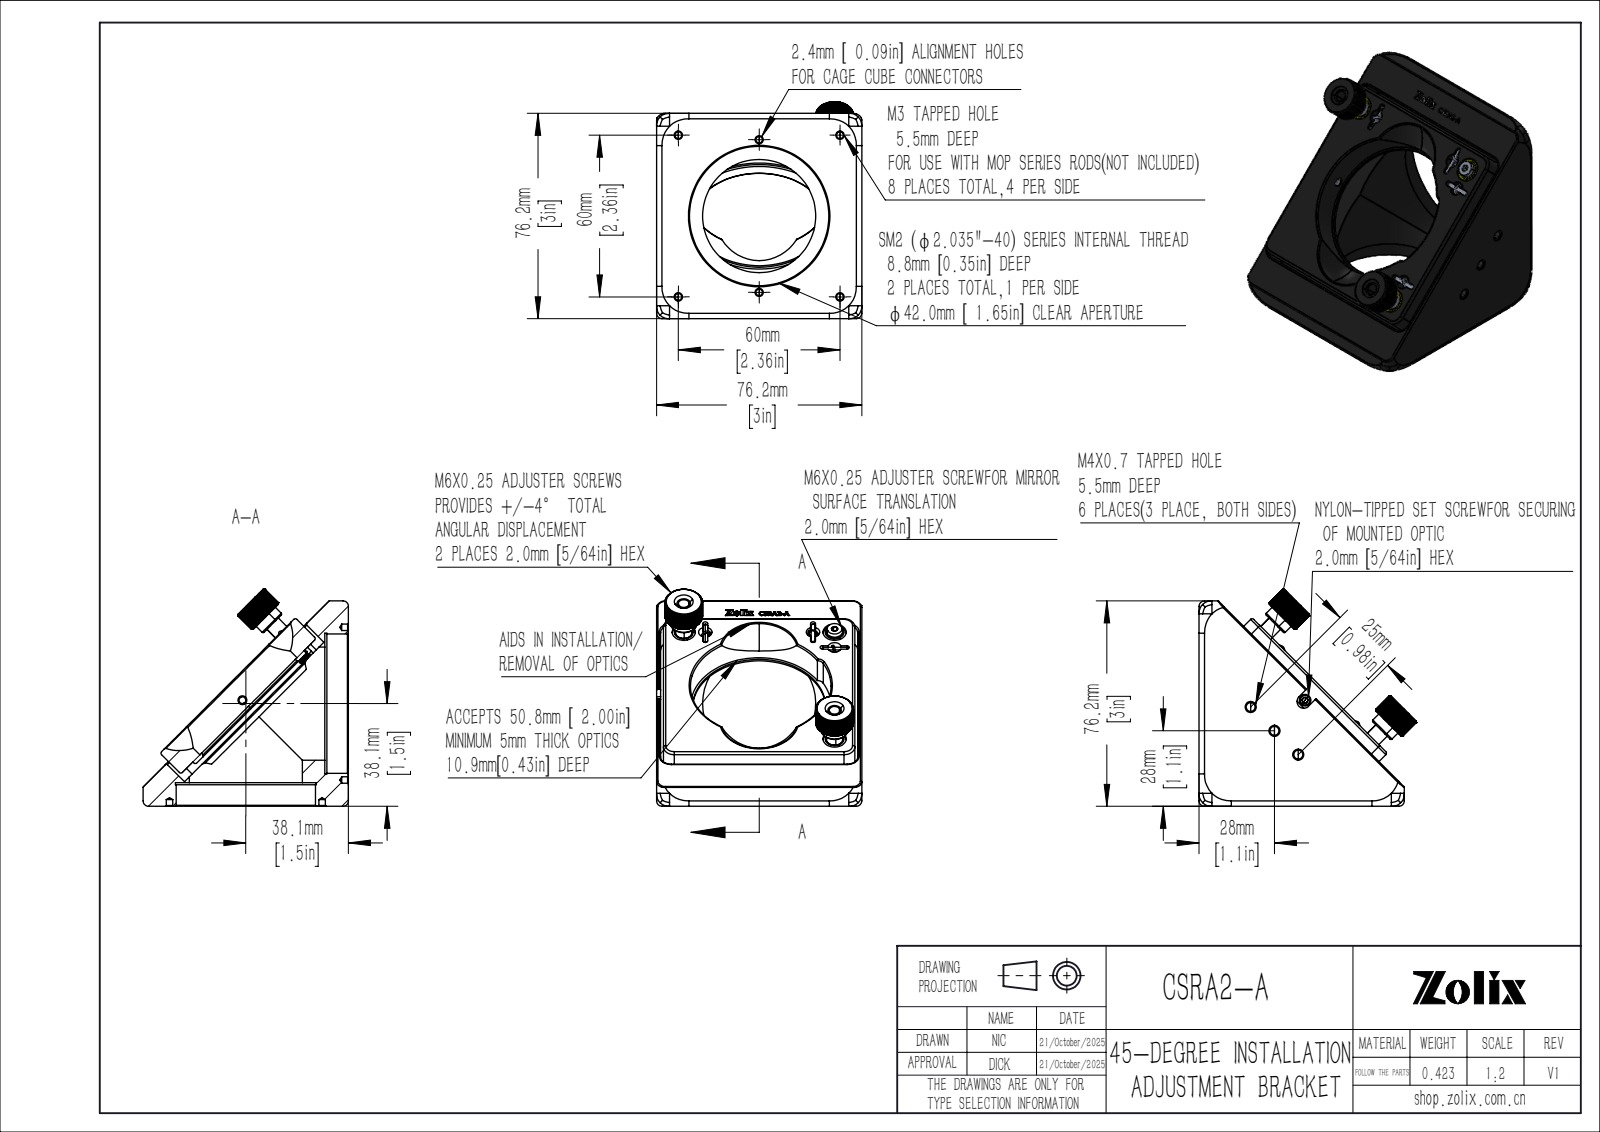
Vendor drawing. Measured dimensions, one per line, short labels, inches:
name: CSRA2-A
written by: SolidWorks 2020 (CONFIG_CONTROL_DESIGN)
unit: in
bodies: 22 solids, 1313 faces (594 planar, 343 cylindrical, 376 other)
size: 3.17 × 3.17 × 3
volume: 9.567 in³; area: 78 in²
holes: 8× ⌀0.098, 5× ⌀0.236, 4× ⌀0.095, 4× ⌀0.107, 4× ⌀0.13, 4× ⌀0.197, 4× ⌀0.201, 3× ⌀0.077, 3× ⌀0.188, 3× ⌀0.339, 3× ⌀0.37, 2× ⌀0.118
bosses: 4× ⌀0.063, 3× ⌀0.36, 3× ⌀0.32, 2× ⌀0.394, 2× ⌀0.339, 1× ⌀2.299, 1× ⌀0.236, 1× ⌀0.157
rounds: 12× R0.02, 8× R0.031, 8× R0.035, 8× R0.157, 7× R0.079, 2× R0.1, 2× R0.276, 1× R0.098
face distances: 3, 0.043, 0.547, 0.118, 0.429, 0.256, 0.374, 0.173, 0.346, 0.102
hole spacings: 0.315, 2.205, 1.183, 1.67, 2.362, 2.582, 1.89, 1.559
